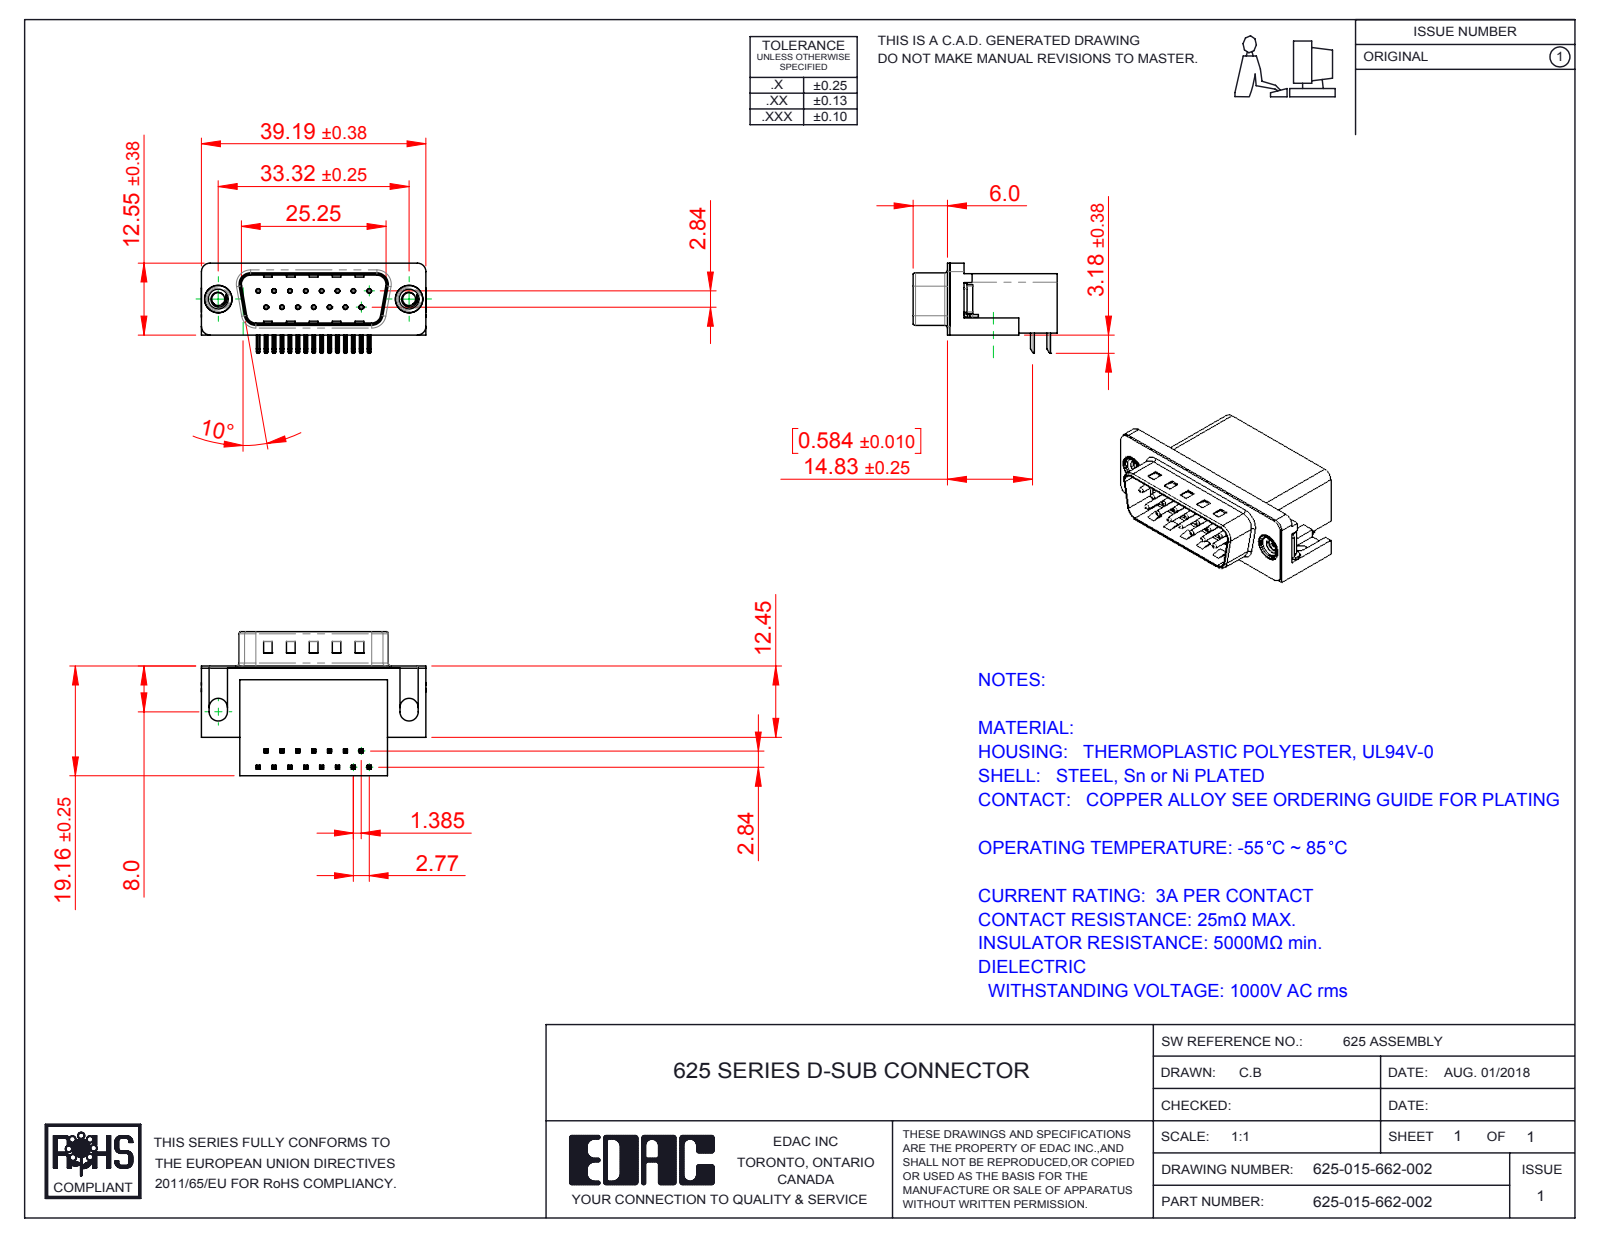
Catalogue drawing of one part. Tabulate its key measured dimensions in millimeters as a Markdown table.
| quantity | value |
| --- | --- |
| part name | 625 Non Board Mount; 625 Contact Bottom; 625 4-40 Threaded Rivet; 625-015-662-002 (+3 more) |
| STEP written by | SolidWorks 2016 (CONFIG_CONTROL_DESIGN) |
| units | millimeters |
| bodies | 21 solids, 1477 faces (895 planar, 443 cylindrical, 139 other) |
| overall size | 39.22 × 25.16 × 15.73 |
| volume | 6 216 mm³ |
| surface area | 6 291 mm² |
| round holes (diameter × count) | 0.35 × 15, 0.8 × 15, 2.26 × 2, 4 × 2, 4.8 × 2, 5 × 2 |
| round bosses / shafts (diameter × count) | 0.75 × 15, 4.9 × 2, 4.75 × 2, 3.9 × 2 |
| partial cylindrical surfaces (radius × count) | 0.25 × 68, 0.12 × 30, 1 × 16, 0.5 × 9, 1.6 × 8, 1.5 × 6, 0.9 × 4, 2 × 4 |
| main face-to-face distances | 0.4, 10.35, 18.76, 2.1, 10.46, 19.16, 1.7, 10.86, 8.76, 16.26 |
| hole center spacings | 3.16, 2.77, 5.54, 8.31, 11.08, 5.03, 5.04, 7.48 |
